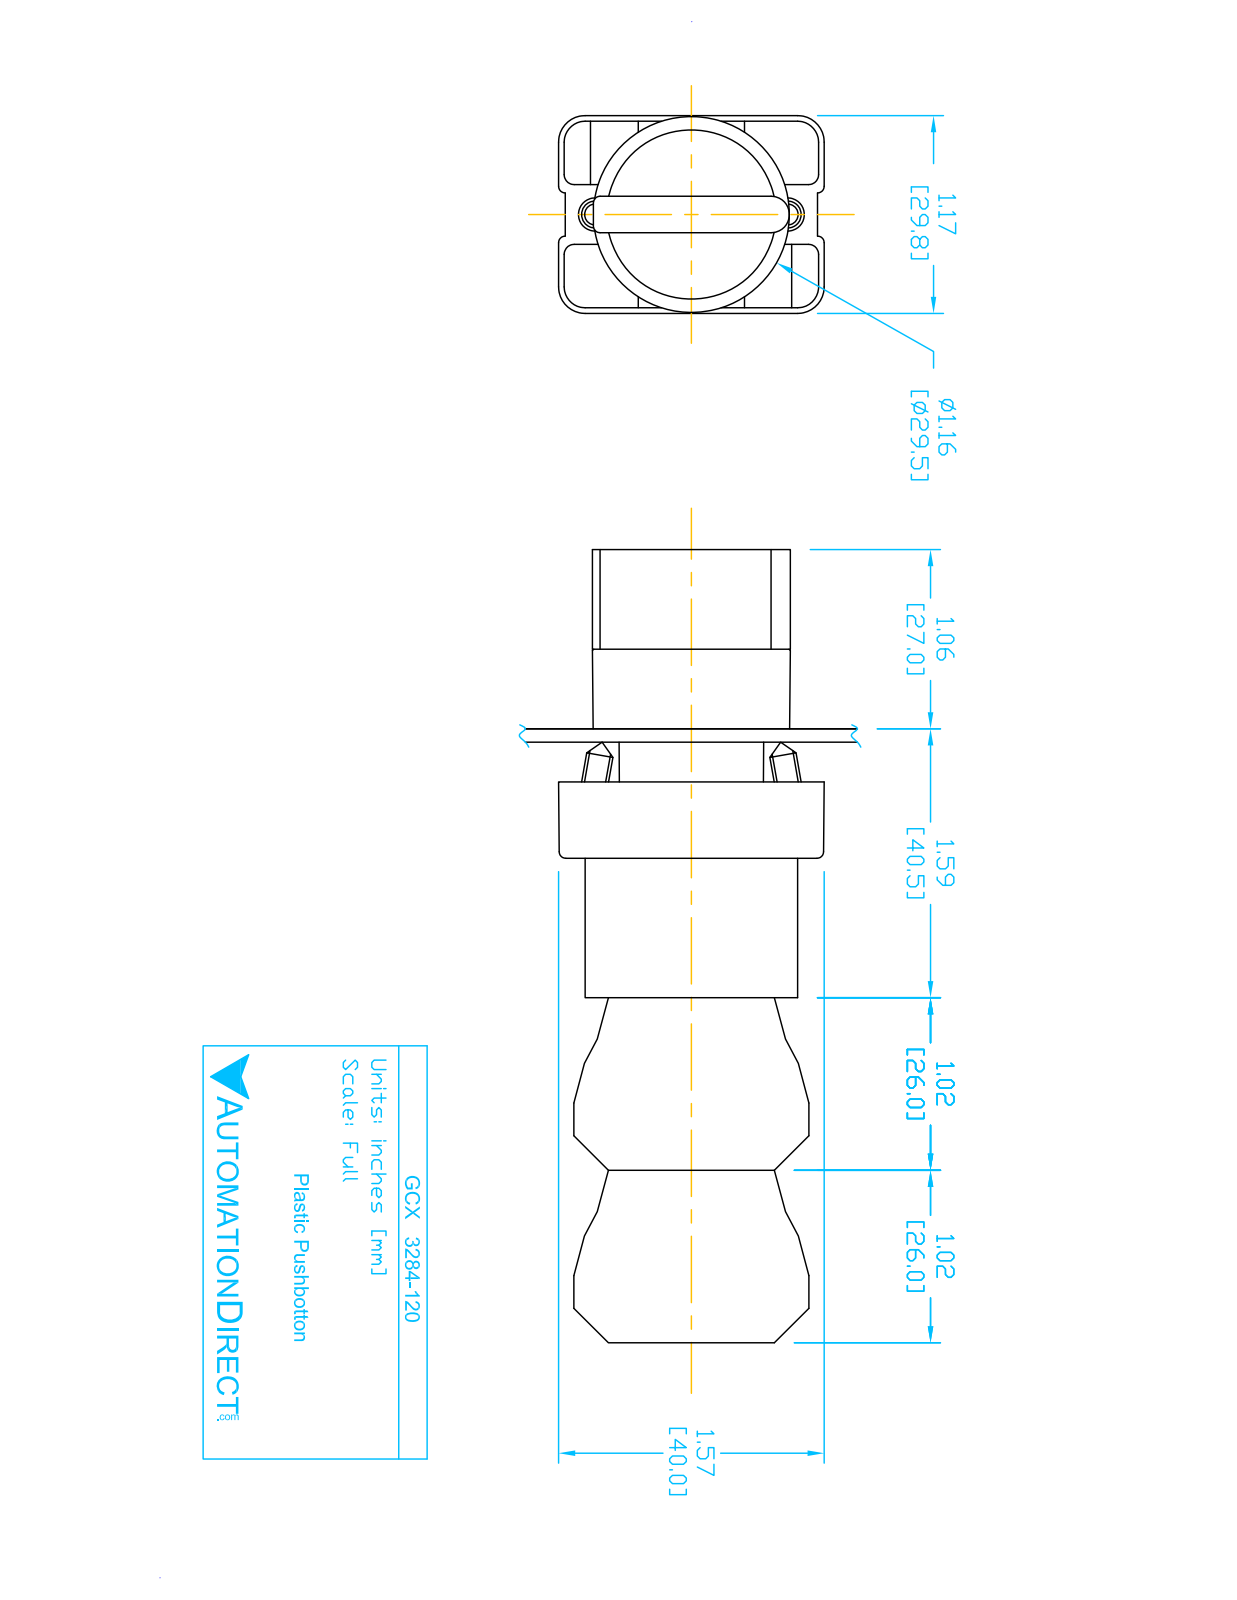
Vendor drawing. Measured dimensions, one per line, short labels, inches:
name: GCX3284 OPERATOR; ecx1040; GCX3284-120; ECX1050 (+2 more)
written by: SolidWorks 2016 (AUTOMOTIVE_DESIGN)
unit: in
bodies: 11 solids, 724 faces (488 planar, 193 cylindrical, 43 other)
size: 4.677 × 1.581 × 1.177
volume: 4.751 in³; area: 59.22 in²
holes: 4× ⌀0.079, 2× ⌀0.087, 2× ⌀0.124, 2× ⌀0.13, 1× ⌀0.197, 1× ⌀0.469, 1× ⌀0.878, 1× ⌀0.888, 1× ⌀1.024
bosses: 4× ⌀0.157, 1× ⌀1.175, 1× ⌀1.004, 1× ⌀0.945, 1× ⌀0.856, 1× ⌀0.78, 1× ⌀0.504
rounds: 24× R0.059, 12× R0.041, 12× R0.124, 12× R0.157, 9× R0.039, 2× R0.02, 2× R0.063, 2× R0.079
face distances: 0.579, 0.593, 1.024, 1.171, 0.014, 0.827, 1.85, 3.043, 2.02, 1.193
hole spacings: 0.236, 1.003, 0.974, 0.472, 0.539, 0.544, 1.083, 0.484
